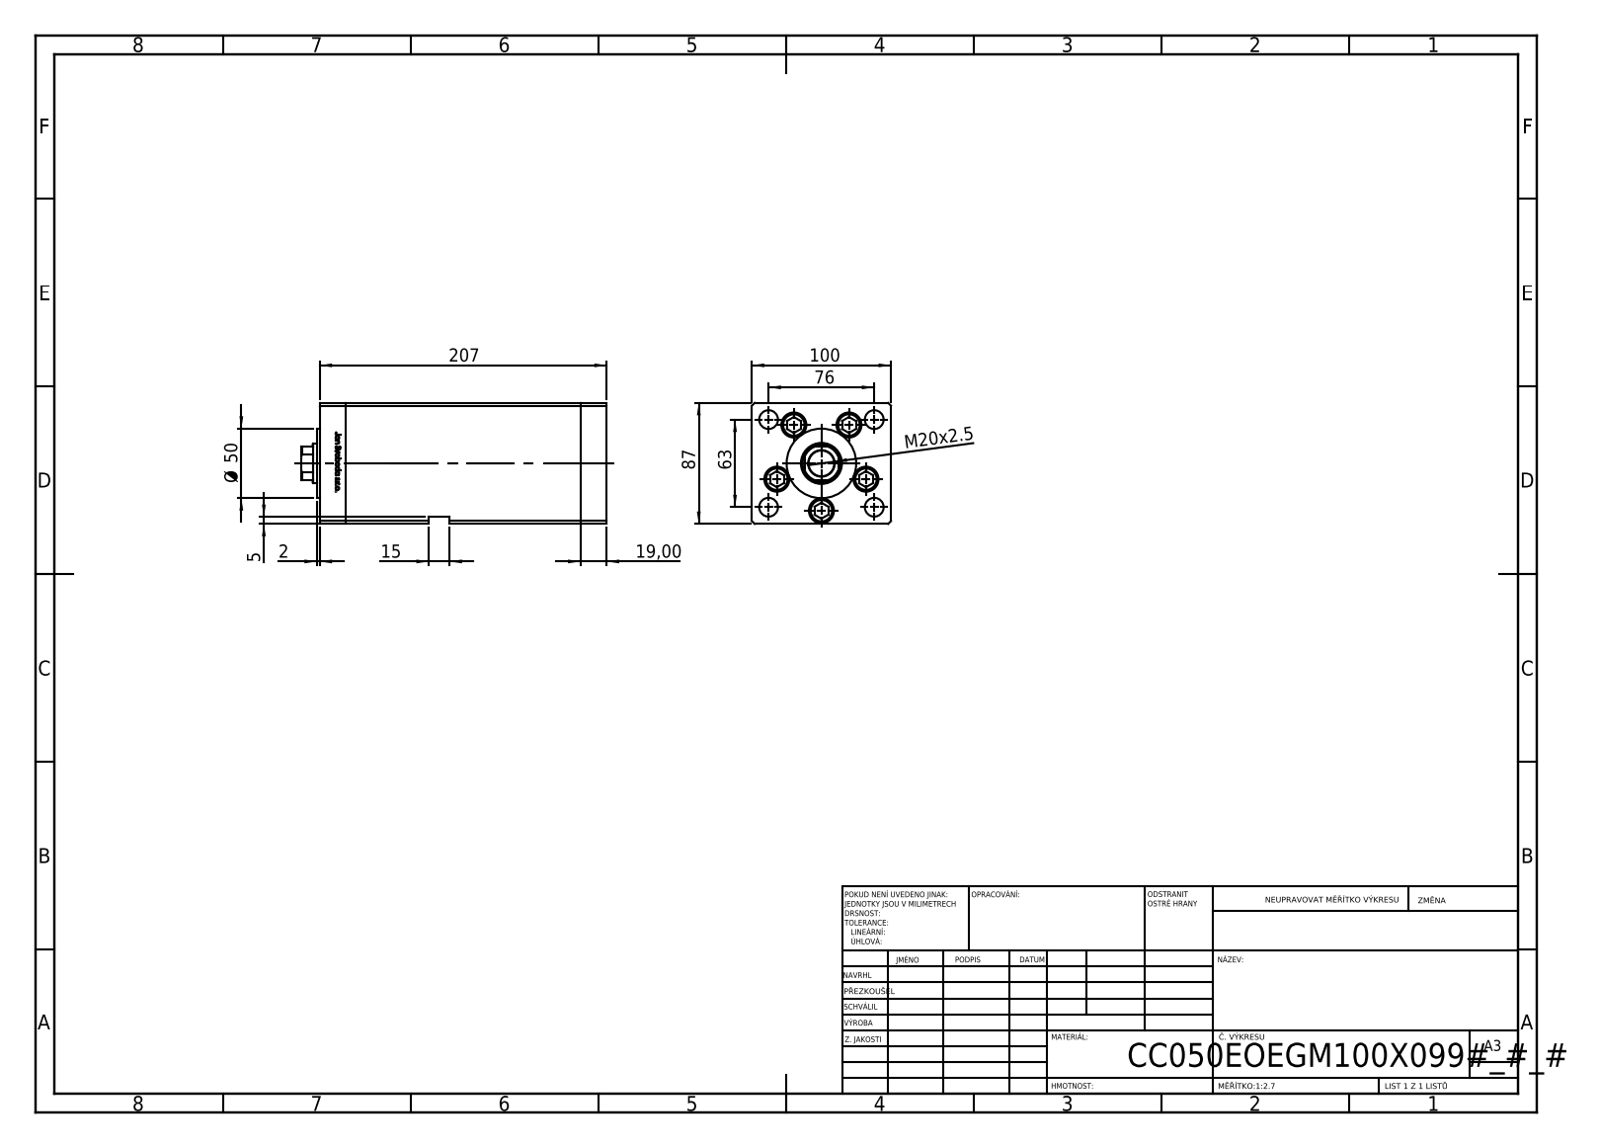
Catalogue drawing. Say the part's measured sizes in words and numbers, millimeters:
The part is named "V220C BACK_E; V220C_E MIDDLE; V220C_VC_E; V220C_FRONT_E (+1 more)". Its 3-D file was written by "SolidWorks 2019 (CONFIG_CONTROL_DESIGN)". It is 14 solids with 1214 faces: 475 planar, 165 cylindrical and 574 other. Overall it measures 219.5 by 100 by 87 millimeters. Its volume is 1 508 000 cubic millimeters and its surface area 233 845 square millimeters. Round holes: 11 of diameter 13.5, 5 of diameter 18, 5 of diameter 18.5, 4 of diameter 12.5, 2 of diameter 2, 2 of diameter 13.16, 1 of diameter 28, 1 of diameter 29.5. Round bosses or shafts: 5 of diameter 17, 5 of diameter 8, 1 of diameter 50. Partial cylindrical surfaces (rounded edges, fillets, slot ends): 2 of radius 0.93, 1 of radius 13.5. The main face-to-face distances are 100, 87, 19, 168.5, 187.5, 34.25, 206.5, 15.25, 153.25, 172.25. The hole center spacings are 34, 18.59, 39.64, 49.36, 57.95, 21.03, 38.08, 39.27.
